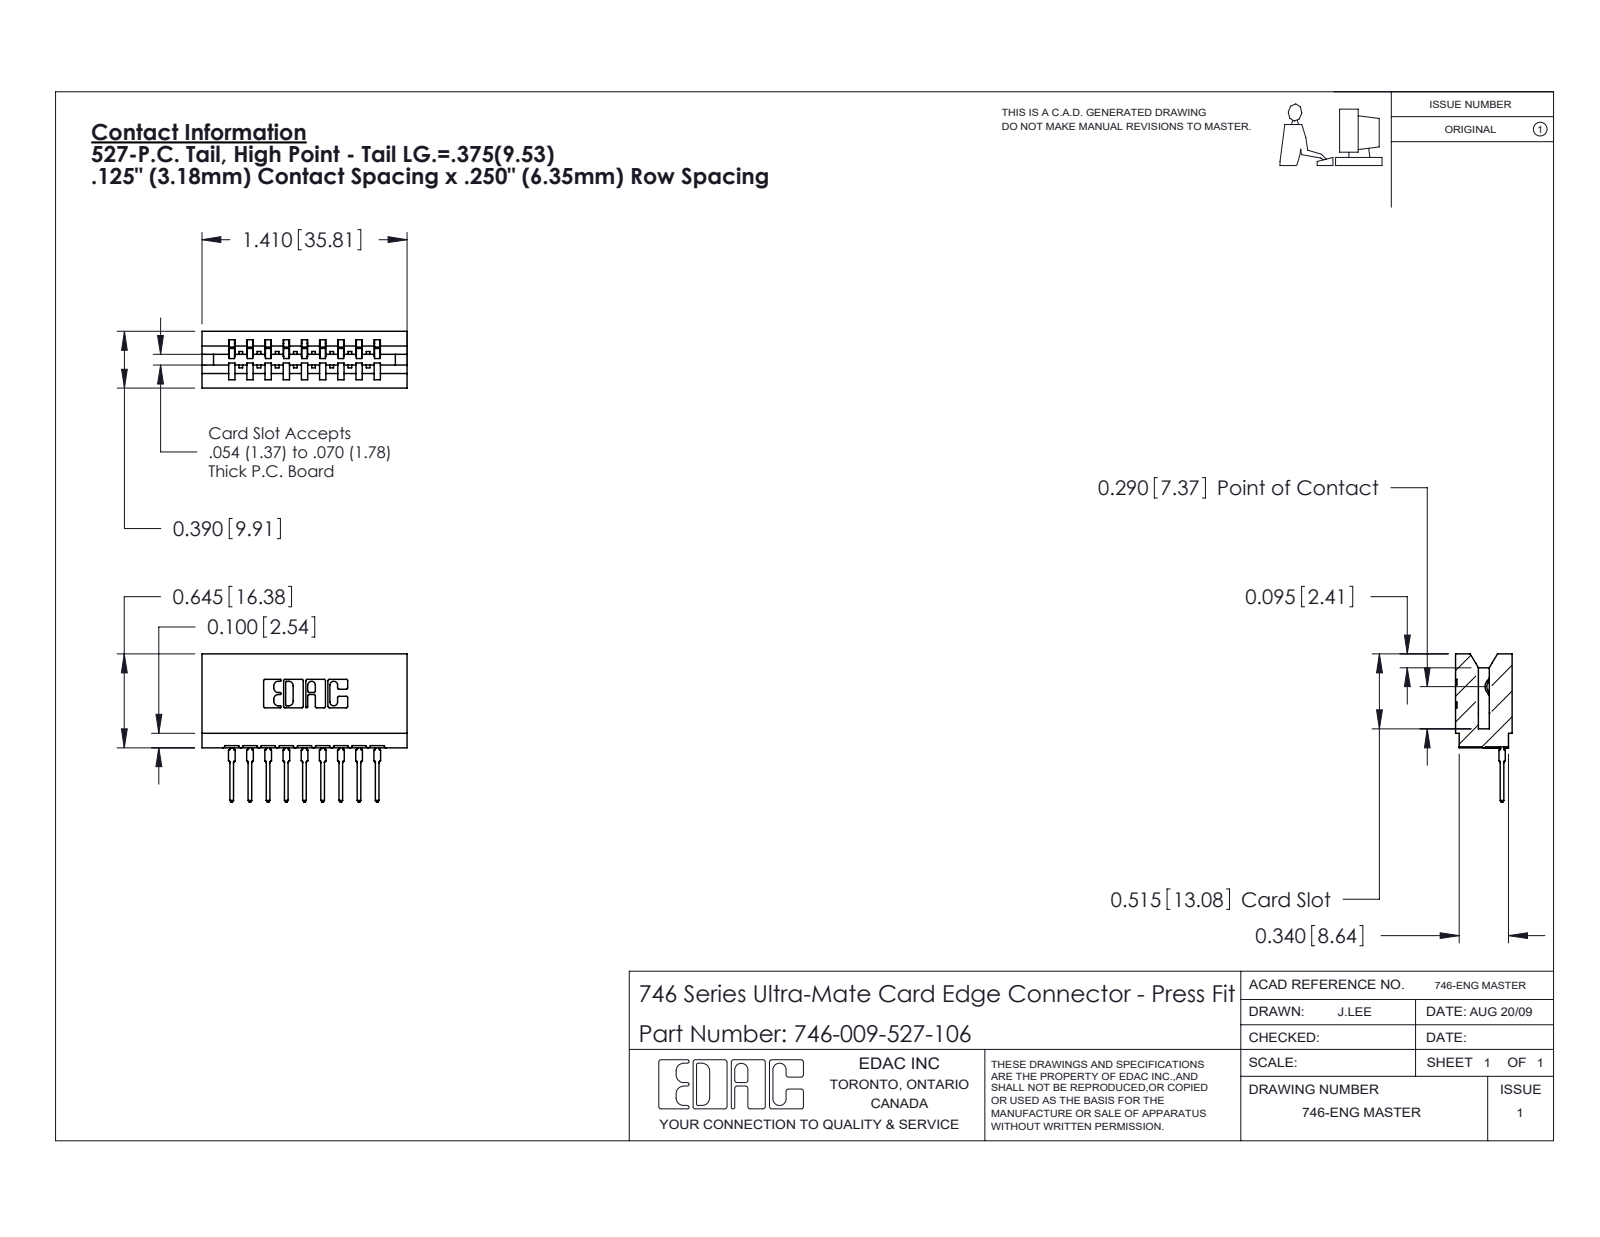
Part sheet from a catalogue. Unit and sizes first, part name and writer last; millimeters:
Units: millimetres
Overall size (bounding box): 35.8 × 25.9 × 9.9
Partial cylindrical surfaces — rounded edges, fillets, slot ends (radius × count): R0.3 ×22, R0.5 ×18, R0.4 ×10, R0.2 ×6, R0.8 ×6, R0.1 ×4, R0.3 ×4, R0.7 ×3
Main face-to-face distances: 6.4, 12.7, 1.1, 8.5, 3.2, 3.2, 1.4, 7.4, 5.3, 19.1
Volume: 3 950 mm³ · Surface area: 5 370 mm²
Bodies: 10 solids, 1070 faces (623 planar, 213 cylindrical, 234 other)
Part name (STEP PRODUCT): 746-009-527-106; 746-292-001_527; 746 Part_.515 Slot Depth - 06
STEP written by: SolidWorks 2020 (CONFIG_CONTROL_DESIGN)
